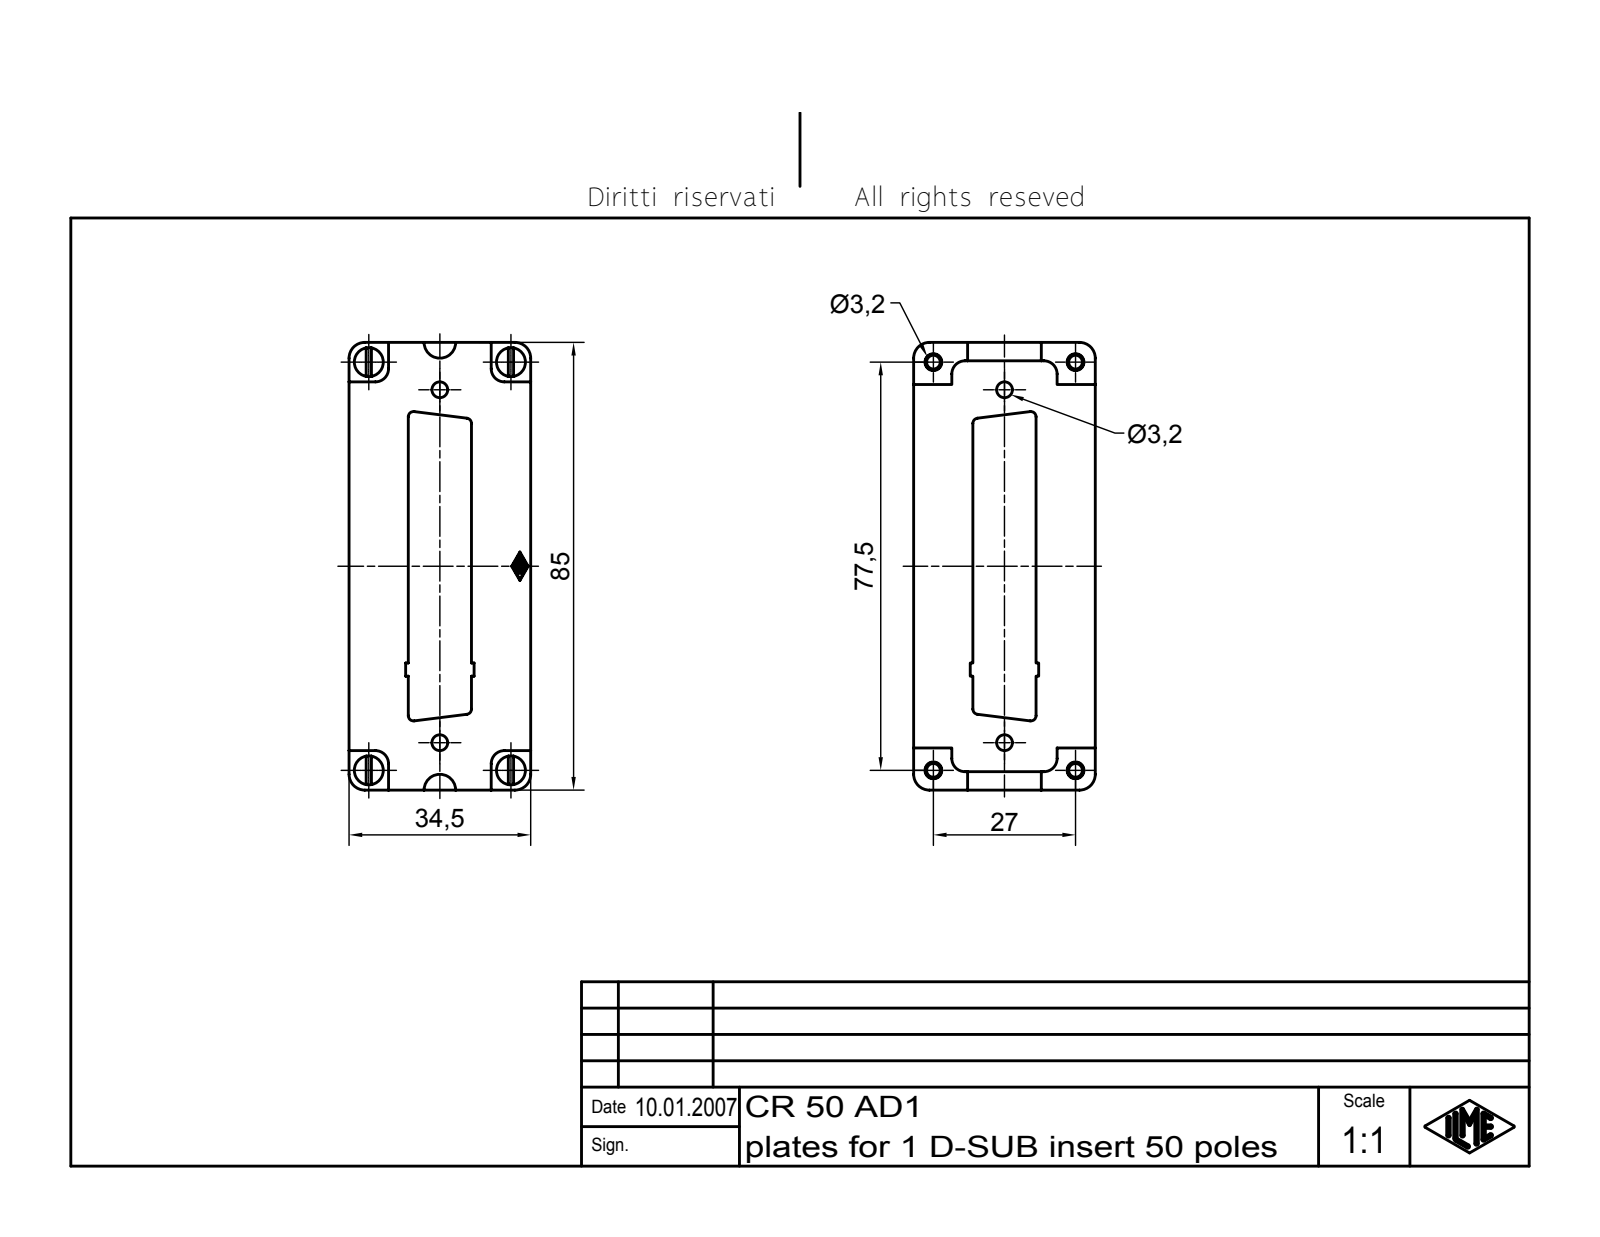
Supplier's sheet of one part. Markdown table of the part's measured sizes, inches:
| quantity | value |
| --- | --- |
| part name | CR 50 AD1 |
| STEP written by | Autodesk Inventor 7 (AUTOMOTIVE_DESIGN) |
| units | inches |
| bodies | 1 solid, 195 faces (117 planar, 62 cylindrical, 16 other) |
| overall size | 3.346 × 1.358 × 0.551 |
| volume | 0.539 in³ |
| surface area | 12 in² |
| round holes (diameter × count) | 0.126 × 4, 0.118 × 2 |
| round bosses / shafts (diameter × count) | 0.217 × 4, 0.118 × 4 |
| partial cylindrical surfaces (radius × count) | 0.004 × 14, 0.098 × 8, 0.118 × 6, 0.039 × 4 |
| main face-to-face distances | 0.118, 0.315, 0.443, 0.915, 0.276, 1.358, 0.079, 0.394, 3.346, 0.039 |
| hole center spacings | 2.894, 0.57, 0.57, 1.063, 3.051, 3.231, 2.638 |
